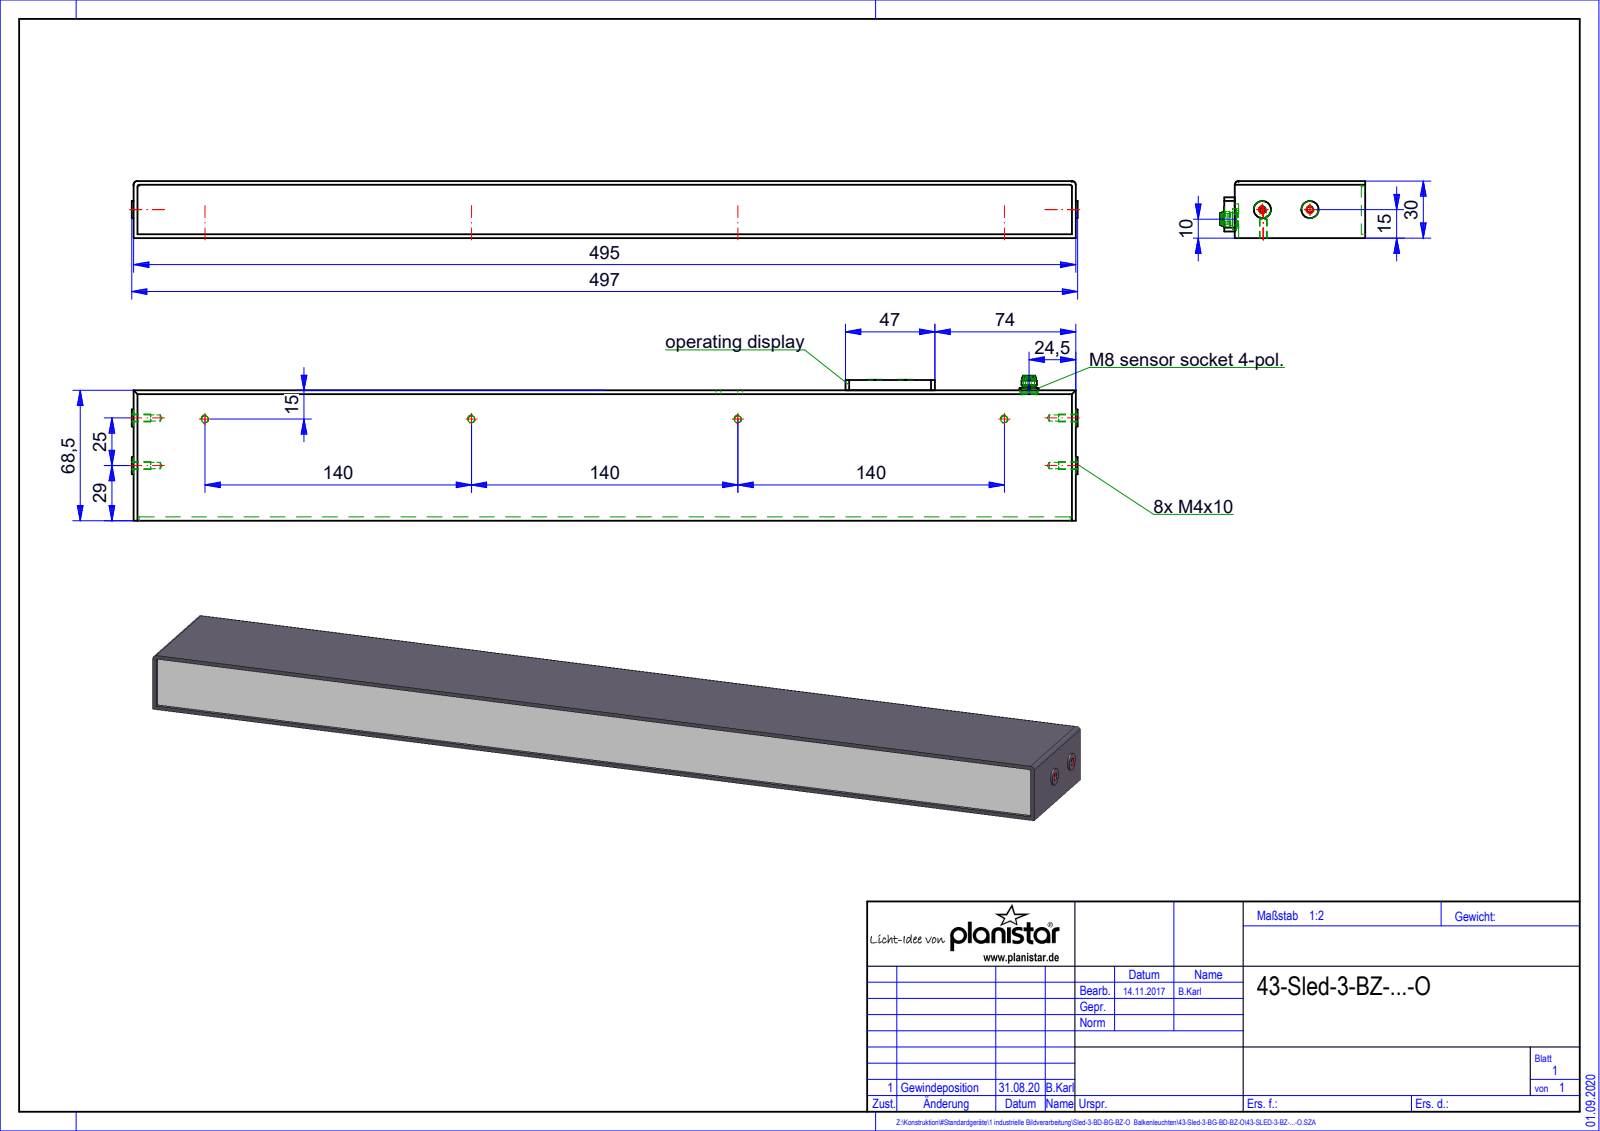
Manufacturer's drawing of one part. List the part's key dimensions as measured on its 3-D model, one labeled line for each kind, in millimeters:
Part name (STEP PRODUCT): Root; Baugruppe_Balkenleuchte; QUADER_3; 09-3391-00-04 (+1 more)
STEP written by: HiCAD 2015 2002.1 Build 408 (AUTOMOTIVE_DESIGN)
Units: millimetres
Bodies: 3 solids, 114 faces (47 planar, 50 cylindrical, 17 other)
Overall size (bounding box): 497 × 76.2 × 30
Volume: 994 589 mm³ · Surface area: 107 773 mm²
Round holes (diameter × count): ⌀3.3 ×6, ⌀4 ×6, ⌀5.8 ×1
Round bosses / shafts (diameter × count): ⌀1 ×4, ⌀8 ×3, ⌀9 ×2, ⌀7.2 ×1, ⌀6.8 ×1, ⌀6.4 ×1
Partial cylindrical surfaces — rounded edges, fillets, slot ends (radius × count): R2 ×7, R1 ×2, R2.5 ×2, R5.5 ×1
Main face-to-face distances: 30, 66.5, 2, 68.5, 28, 495, 26, 74, 72, 5.5
Hole centre spacings: 140, 280, 25, 420
